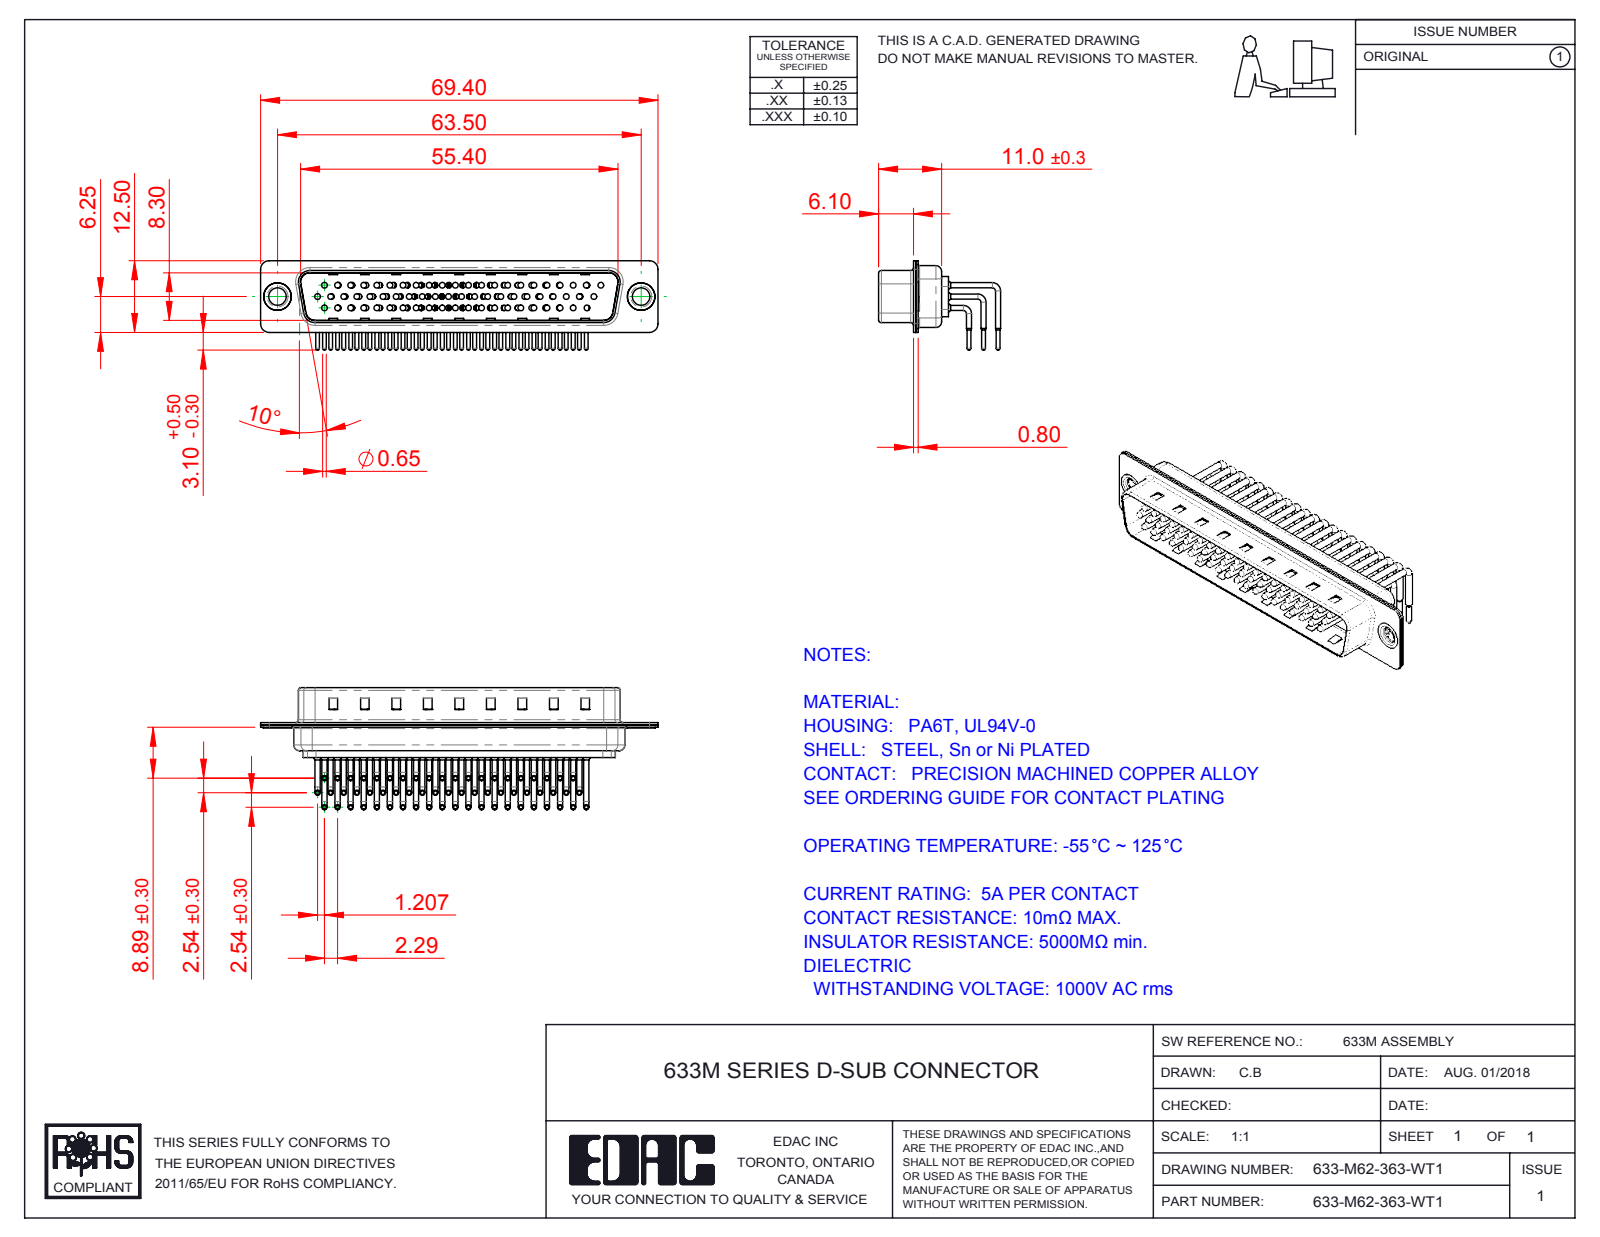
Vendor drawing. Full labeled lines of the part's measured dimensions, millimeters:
Part name (STEP PRODUCT): 633-M62-363-WT1; 633M Housing_62 Contacts; 633M Thru Hole Rivet; 633M Shell Rear_62 Contacts (+4 more)
STEP written by: SolidWorks 2016 (CONFIG_CONTROL_DESIGN)
Units: millimetres
Bodies: 67 solids, 7206 faces (4171 planar, 2357 cylindrical, 678 other)
Overall size (bounding box): 69.4 × 21.32 × 15.6
Volume: 4 269 mm³ · Surface area: 13 496 mm²
Round holes (diameter × count): ⌀1 ×62, ⌀1.7 ×62, ⌀2 ×62, ⌀3.05 ×2, ⌀4 ×2, ⌀4.8 ×2
Round bosses / shafts (diameter × count): ⌀0.9 ×124, ⌀1.5 ×62, ⌀0.65 ×62, ⌀1 ×56, ⌀5 ×2, ⌀4.9 ×2, ⌀3.55 ×2
Partial cylindrical surfaces — rounded edges, fillets, slot ends (radius × count): R1.01 ×62, R1.5 ×16, R2 ×12, R0.5 ×8, R1.6 ×8, R0.25 ×4, R0.6 ×4, R0.65 ×4
Main face-to-face distances: 0.4, 0.85, 9.55, 8.7, 1.5, 1.9, 1.25, 10.4, 0.35, 0.45
Hole centre spacings: 7.24, 2.32, 2.41, 4.13, 9.65, 4.83, 14.48, 11.04
